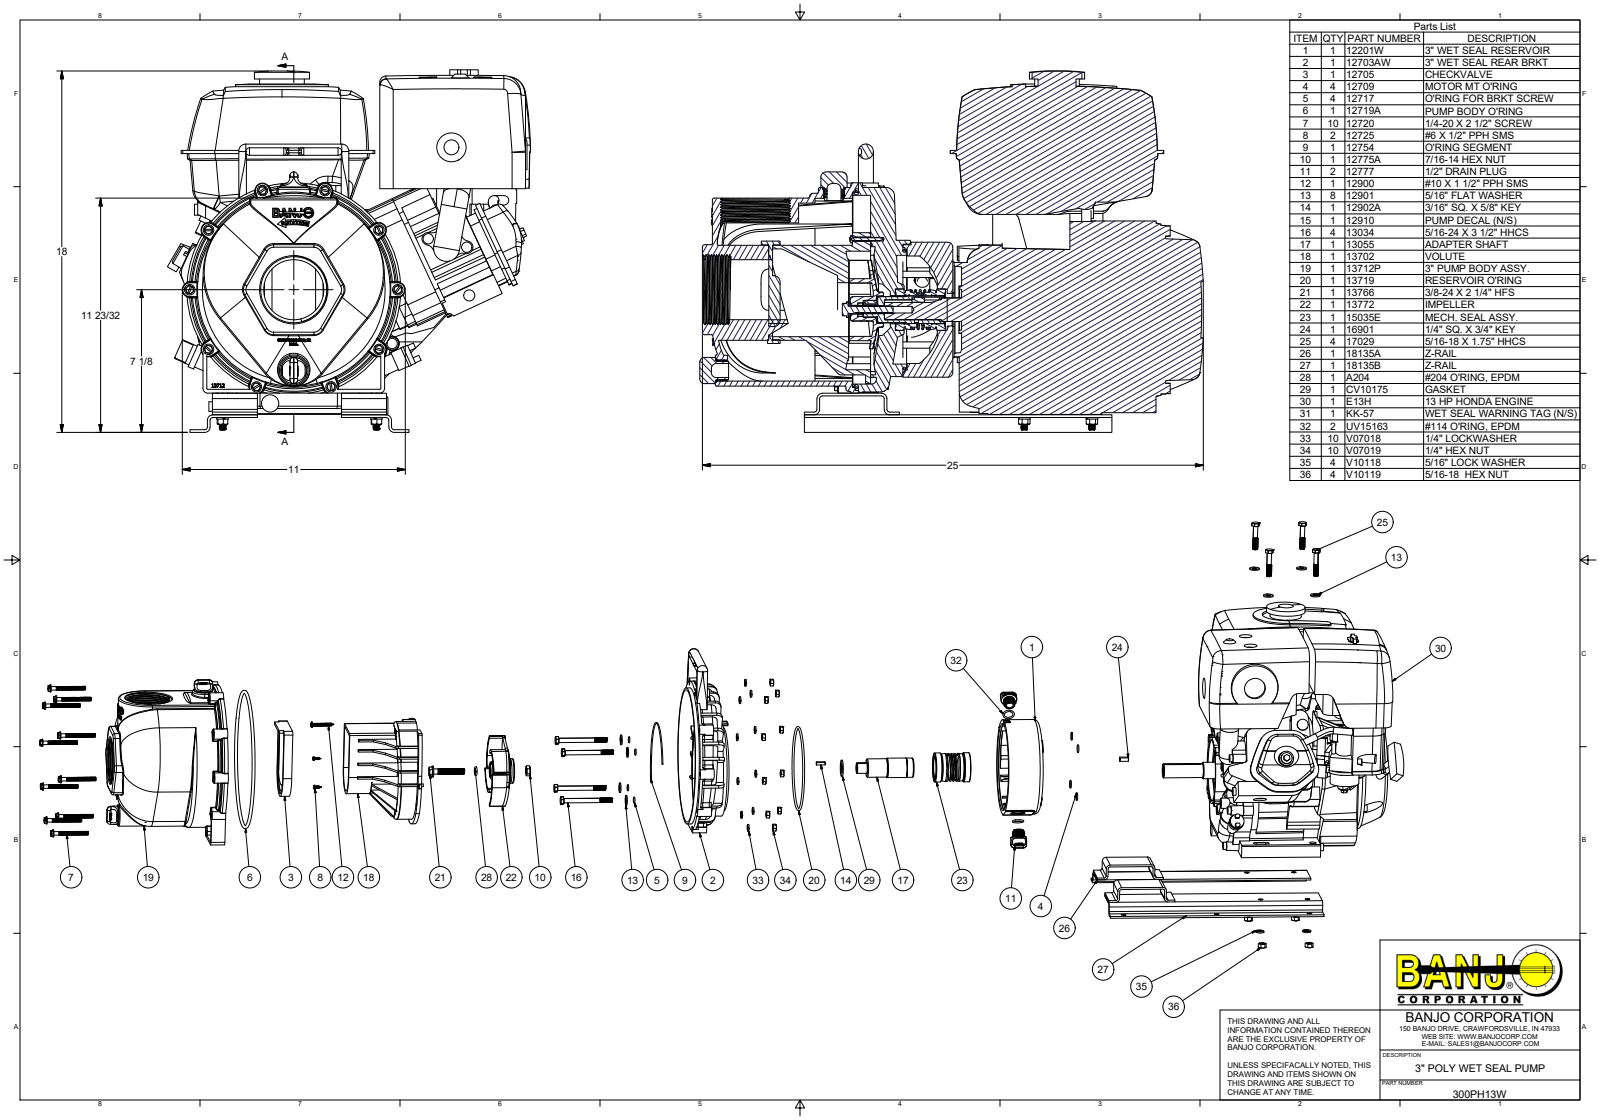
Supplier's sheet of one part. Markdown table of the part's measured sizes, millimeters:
| quantity | value |
| --- | --- |
| part name | 12703AWV; 12703AWX; 12703AW; 12201WX (+8 more) |
| STEP written by | Autodesk Inventor 2016 (AUTOMOTIVE_DESIGN) |
| units | millimeters |
| bodies | 115 solids, 11159 faces (2921 planar, 3170 cylindrical, 5068 other) |
| overall size | 657.54 × 461.24 × 460.52 |
| volume | 37 390 000 mm³ |
| surface area | 2 798 000 mm² |
| round holes (diameter × count) | 8.73 × 16, 4.98 × 10, 6.4 × 10, 6.86 × 10, 11.91 × 8, 14.25 × 8, 5.59 × 7, 8 × 6, 6.41 × 4, 7.95 × 4, 8.18 × 4, 2.87 × 2 |
| round bosses / shafts (diameter × count) | 7.02 × 80, 6.82 × 60, 13 × 17, 13.21 × 10, 12.42 × 10, 6.35 × 10, 17.48 × 8, 9.68 × 8 |
| partial cylindrical surfaces (radius × count) | 0.76 × 140, 3.17 × 77, 0.38 × 63, 1.52 × 51, 20 × 43, 4.76 × 35, 10 × 35, 6.35 × 27 |
| main face-to-face distances | 3.42, 0.5, 3.92, 290.66, 287.24, 286.74, 6.35, 3.41, 27.43, 295.62 |
| hole center spacings | 78.4, 132.08, 195.5, 17.52, 45.98, 63.5, 65.02, 89.8 |
